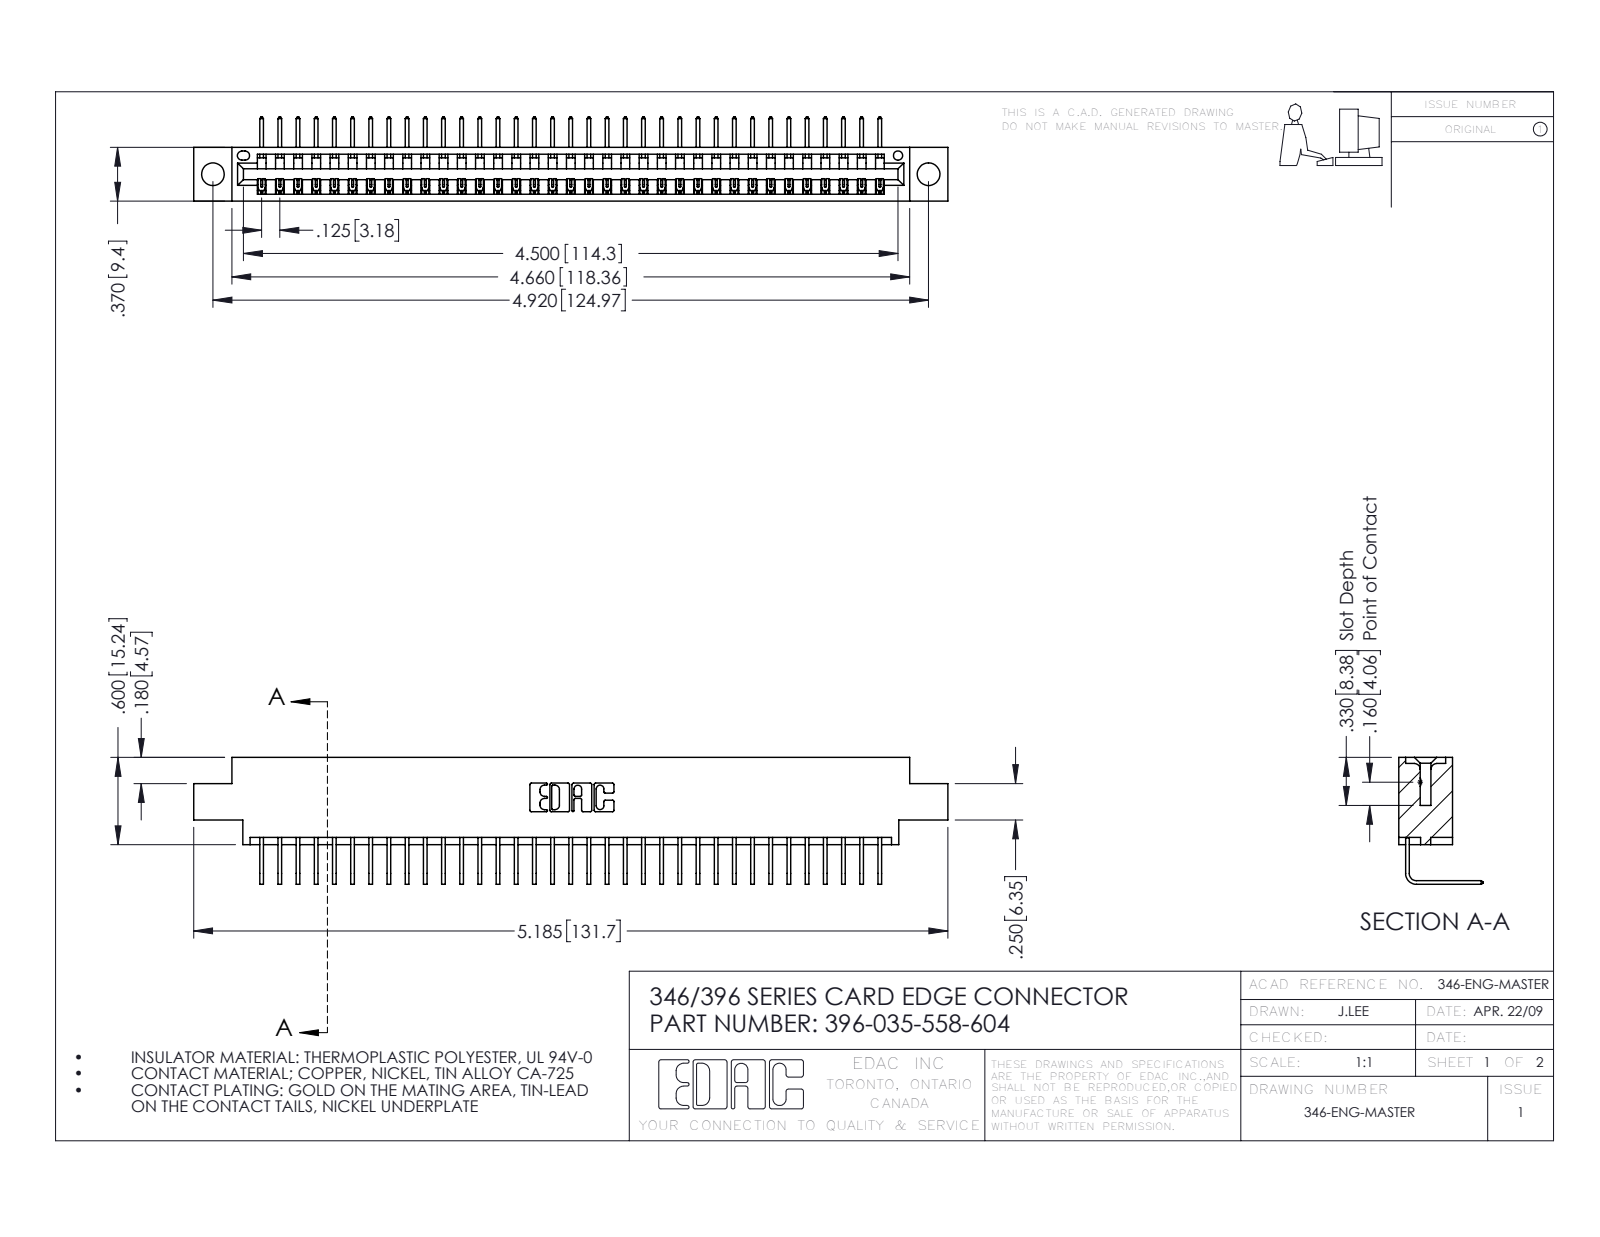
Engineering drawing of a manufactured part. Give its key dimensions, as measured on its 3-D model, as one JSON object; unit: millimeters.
{"part_name": "346 Part_0.170 Offset - 0.156 Dia-TH; 396-035-558-604; 345-292-001_558 Tail - 2", "step_written_by": "SolidWorks 2016 (CONFIG_CONTROL_DESIGN)", "units": "millimeters", "bodies": {"solids": 36, "faces": 2226, "planar": 1550, "cylindrical": 676, "other": 0}, "overall_size": [131.7, 22.2, 14.7], "volume_mm3": 12400, "surface_area_mm2": 16120, "round_holes": [[4, 2], [1.6, 1]], "partial_cylinders_radius": [[0.2, 70], [0.3, 22], [0.2, 6], [0.8, 6], [0.7, 3], [0.8, 2], [1, 2], [0.4, 1]], "face_to_face_distances": [8.2, 1.2, 9.4, 6.4, 7.6, 0.6, 1.8, 3.8, 5.6, 2.5], "hole_center_spacings": [6.2, 119.7, 125]}
